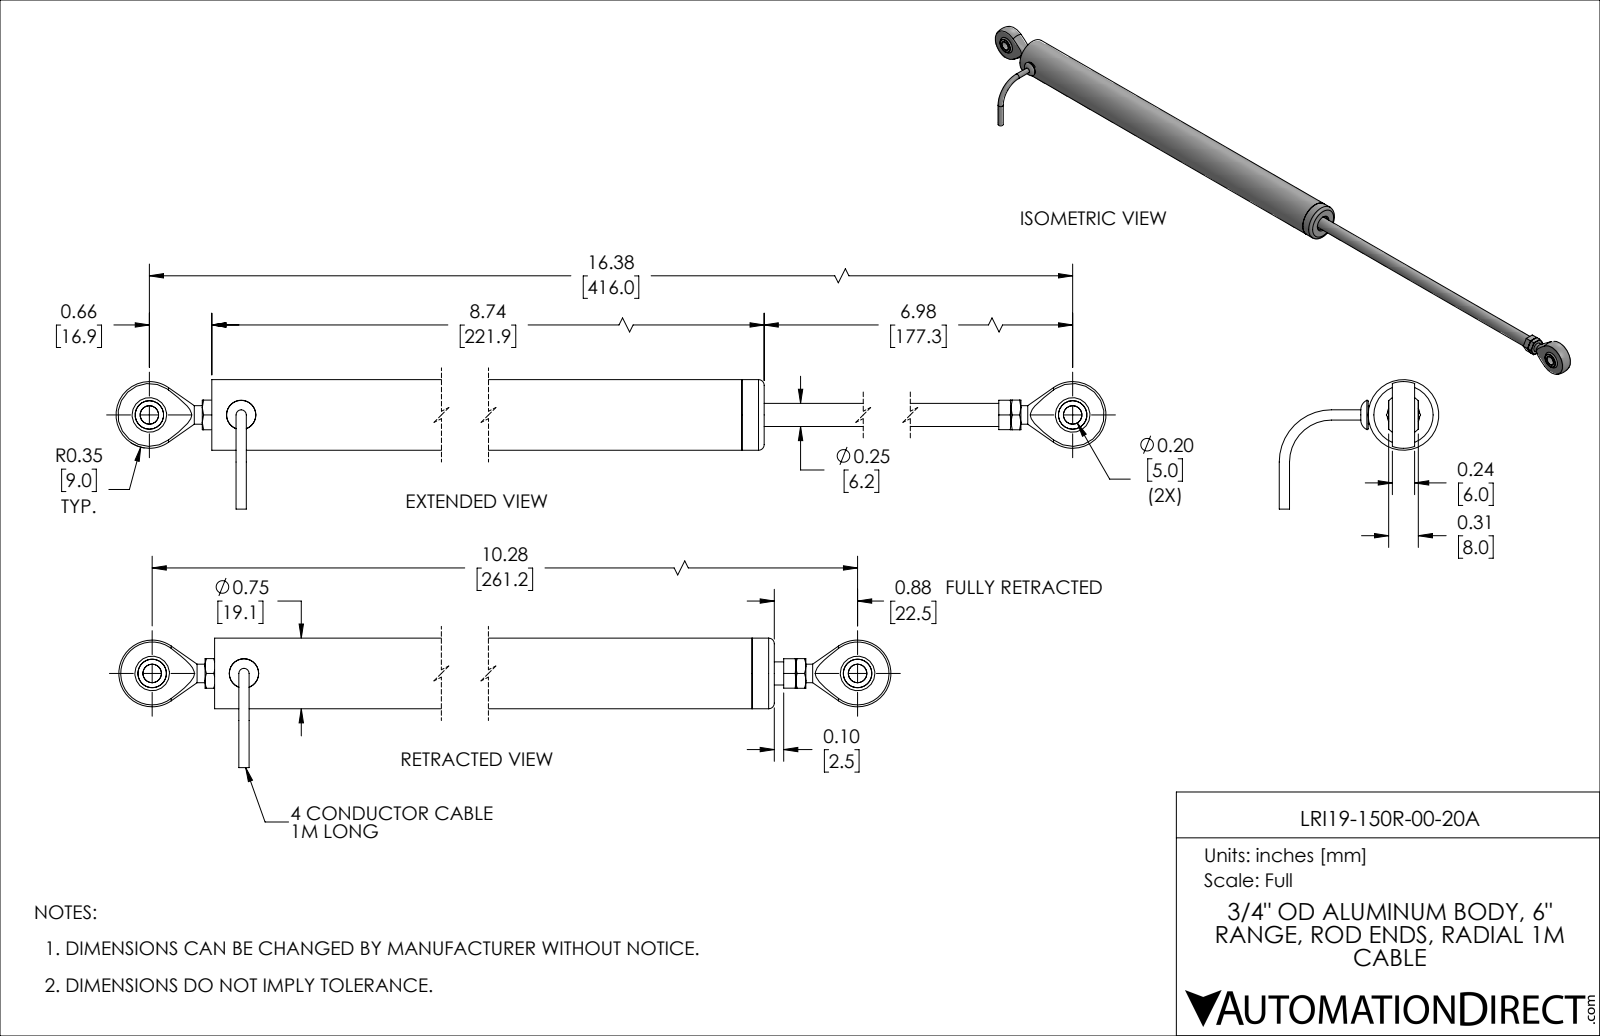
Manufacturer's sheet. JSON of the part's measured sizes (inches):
{"part_name": "LRI19-150R-00-20A", "step_written_by": "SolidWorks 2019 (AUTOMOTIVE_DESIGN)", "units": "inches", "bodies": {"solids": 13, "faces": 157, "planar": 58, "cylindrical": 34, "other": 65}, "overall_size": [10.993, 1.695, 1.375], "volume_in3": 1.716, "surface_area_in2": 57.95, "round_holes": [[0.197, 3], [0.109, 1], [0.165, 1], [0.188, 1], [0.193, 1], [0.221, 1], [0.307, 1], [0.62, 1], [0.625, 1], [0.65, 1], [0.71, 1], [0.725, 1]], "round_bosses_or_shafts": [[0.75, 1], [0.7, 1], [0.624, 1], [0.246, 1], [0.223, 1], [0.218, 1], [0.109, 1]], "face_to_face_distances": [0.236, 0.105, 8.626, 8.731, 8.495, 8.39, 0.236, 0.315, 0.039, 0.276], "hole_center_spacings": [0.975, 9.309, 10.284]}
